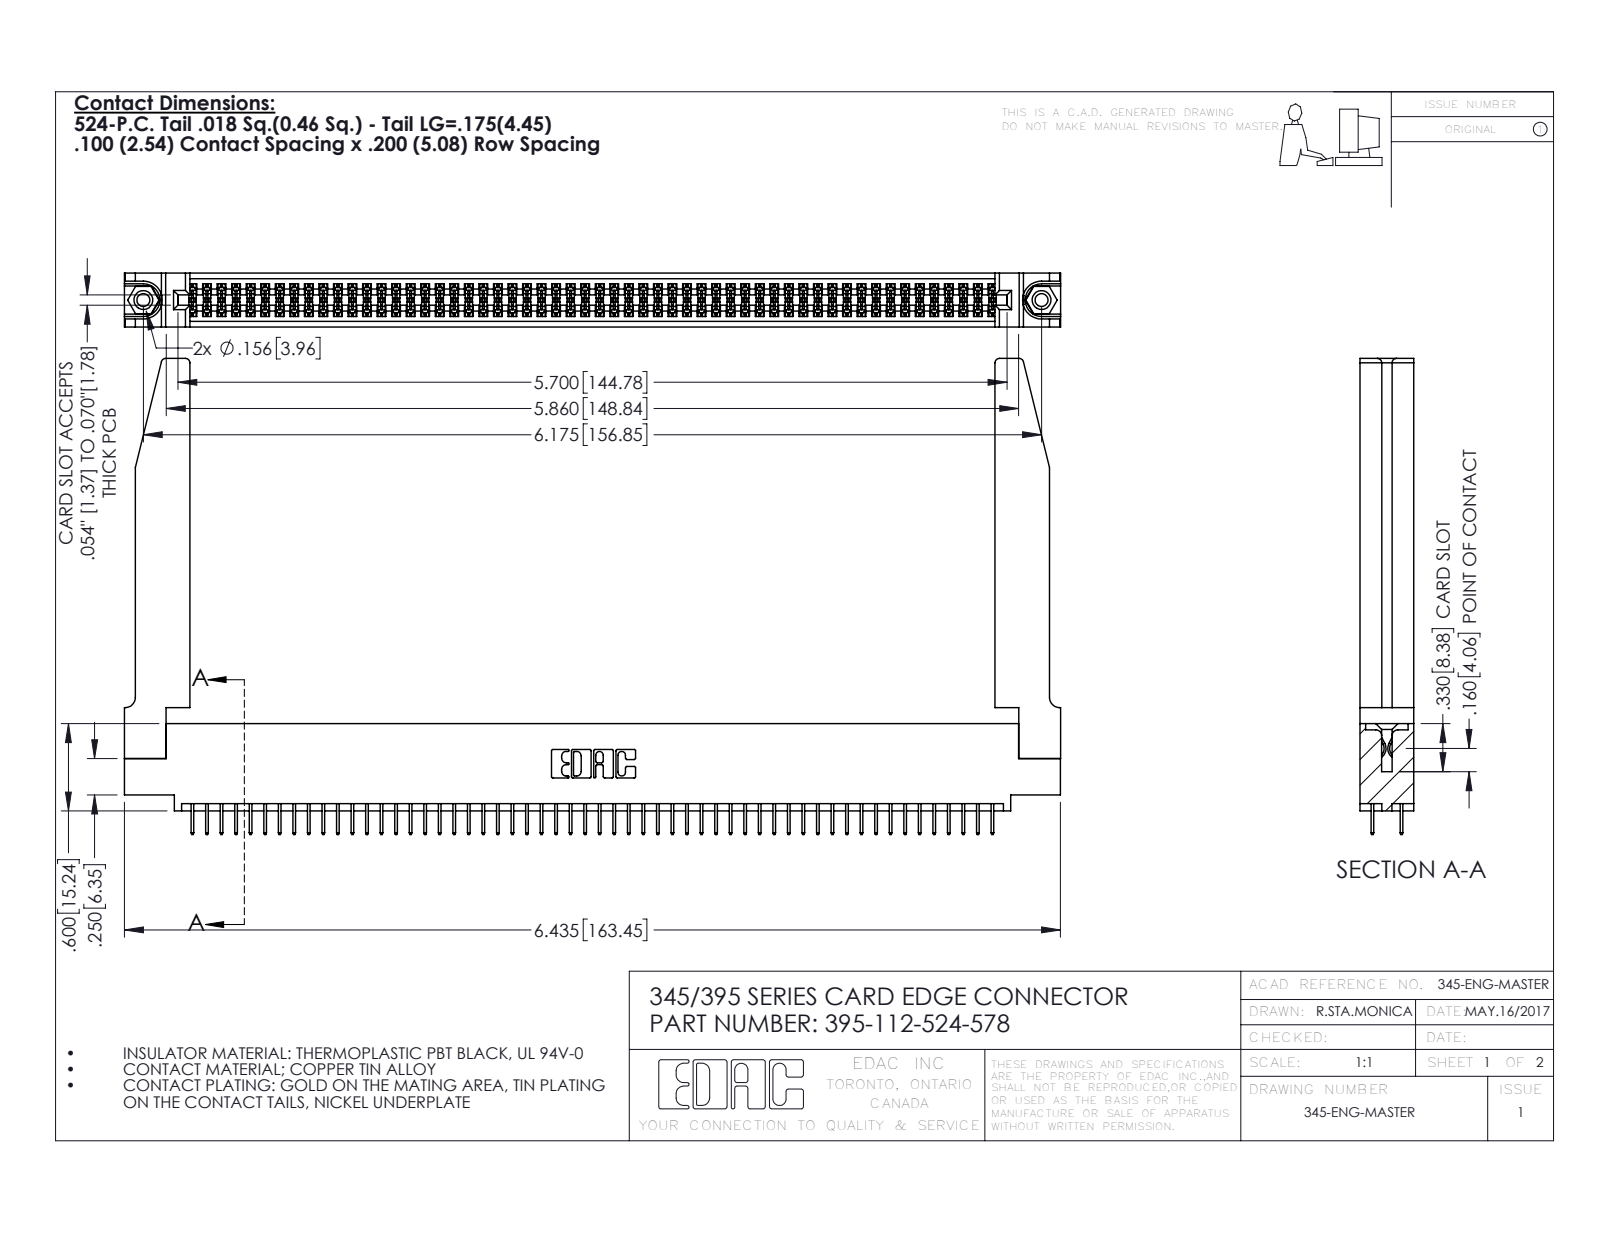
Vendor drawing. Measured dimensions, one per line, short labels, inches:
name: 345-250-001_345-250-001-102; 345-220-078_345-220-078; 345 Part_0.110 Offset - 0.156 Dia-TH; 395-112-524-578 (+1 more)
written by: SolidWorks 2016 (CONFIG_CONTROL_DESIGN)
unit: in
bodies: 117 solids, 6412 faces (4594 planar, 1766 cylindrical, 52 other)
size: 6.436 × 3.272 × 0.37
volume: 1.436 in³; area: 46.6 in²
holes: 2× ⌀0.089, 2× ⌀0.125, 2× ⌀0.156, 1× ⌀0.064
bosses: 2× ⌀0.155
rounds: 168× R0.006, 22× R0.01, 8× R0.03, 6× R0.007, 6× R0.031, 3× R0.026, 2× R0.014, 2× R0.019
face distances: 0.072, 0.37, 0.298, 0.2, 0.098, 0.272, 0.025, 0.225, 0.072, 0.175
hole spacings: 0.27, 5.939, 6.175
